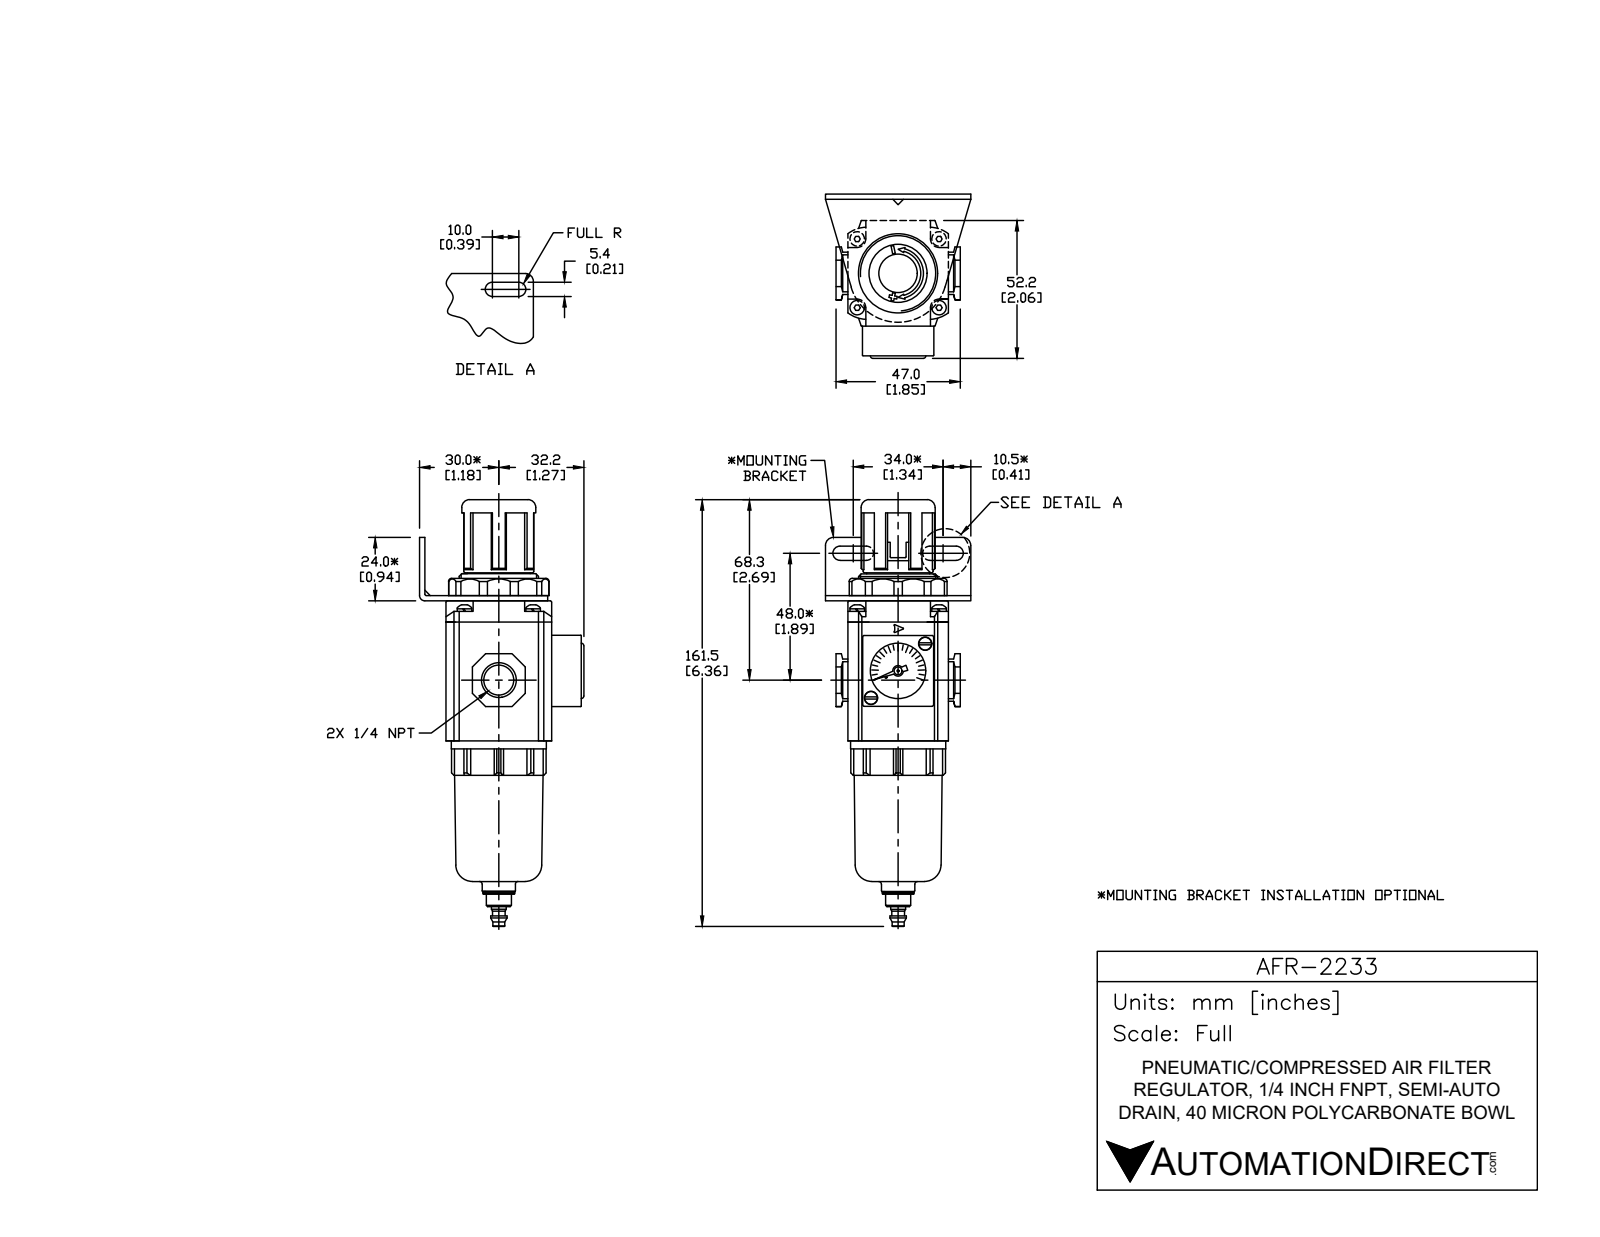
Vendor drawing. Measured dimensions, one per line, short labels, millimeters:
name: AFR-2233
written by: SolidWorks 2015 (CONFIG_CONTROL_DESIGN)
unit: mm
bodies: 15 solids, 548 faces (329 planar, 159 cylindrical, 60 other)
size: 161.2 × 62 × 55
volume: 132 390 mm³; area: 40 712 mm²
holes: 7× ⌀3, 1× ⌀2, 1× ⌀11.13, 1× ⌀21, 1× ⌀22, 1× ⌀25.5, 1× ⌀30
bosses: 4× ⌀5.5, 2× ⌀2.7, 1× ⌀28, 1× ⌀26, 1× ⌀23.8, 1× ⌀14, 1× ⌀12.6, 1× ⌀12
rounds: 12× R1, 10× R1.2, 6× R3.25, 4× R0.3, 4× R2.75, 4× R12, 3× R0.2, 1× R2
face distances: 2, 55, 40, 53, 38, 39, 10, 1, 50, 11
hole spacings: 20.23, 14.5, 26, 31, 40.46, 28.99
